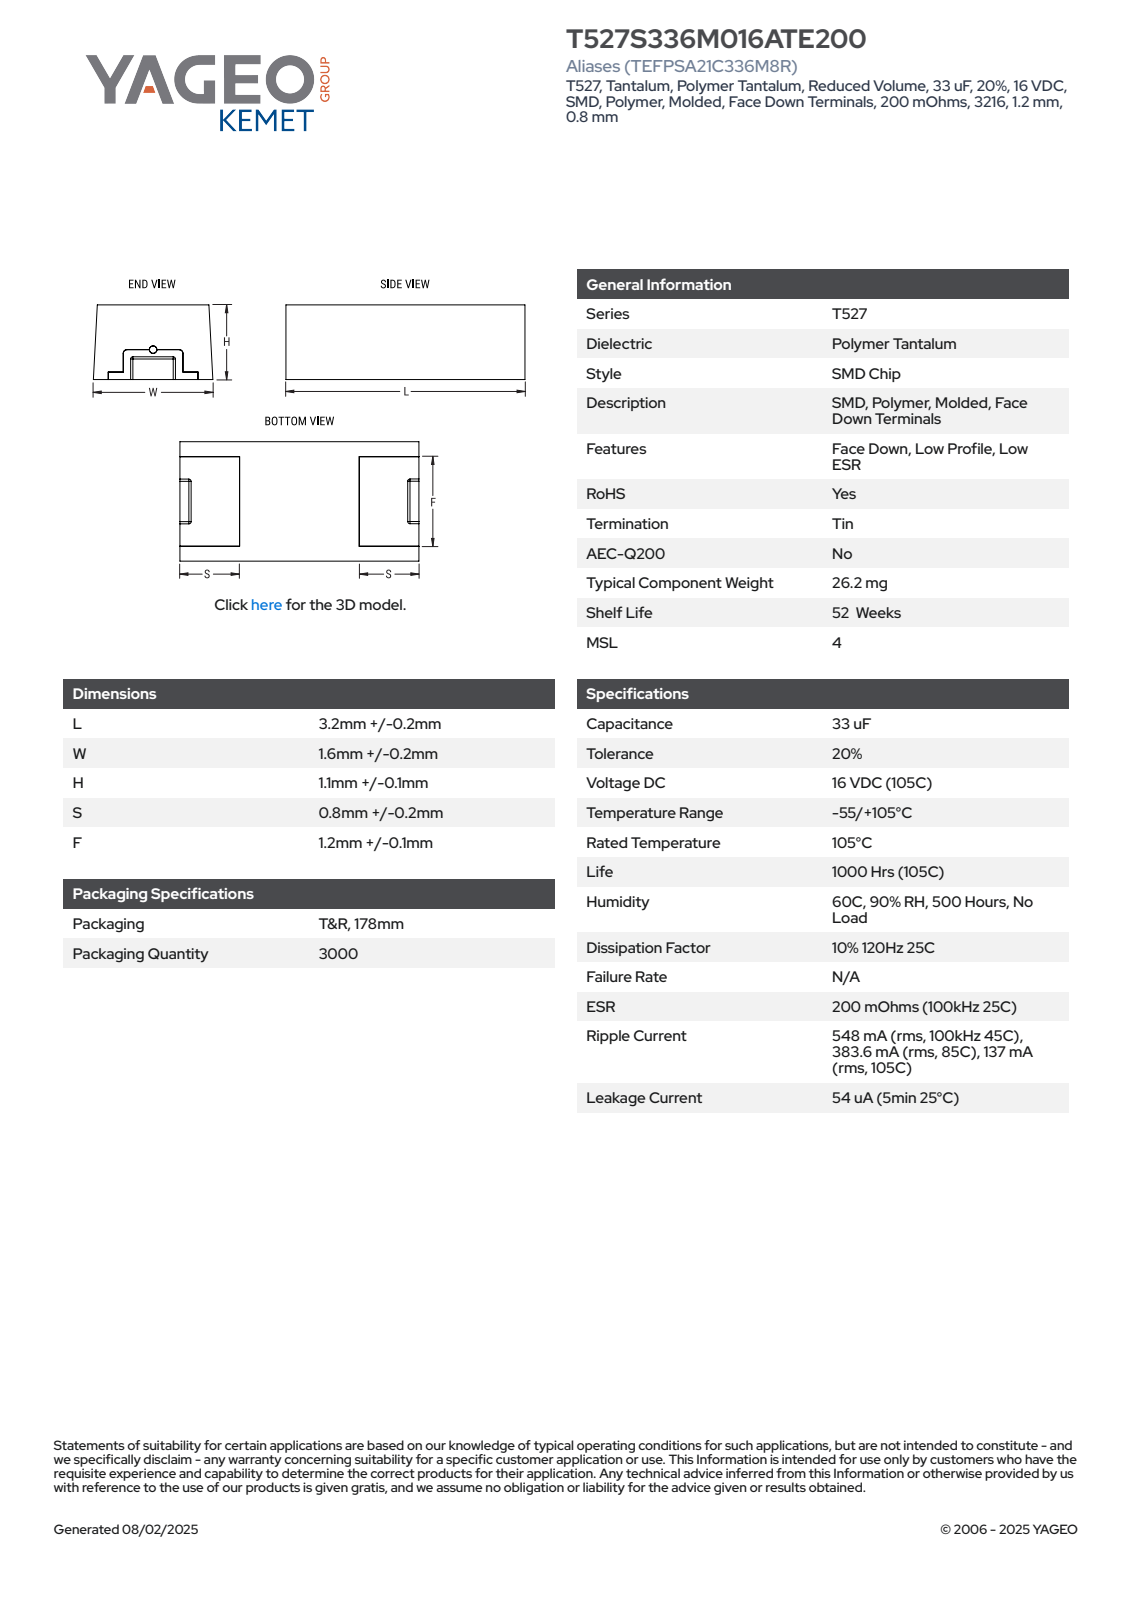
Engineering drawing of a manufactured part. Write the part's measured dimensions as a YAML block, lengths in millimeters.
part_name: "CTS_TCBFD_3216_L3.4W1.8H1.2S0.8F1.3"
step_written_by: "SolidWorks 2020 (AUTOMOTIVE_DESIGN)"
units: millimeters
bodies: {solids: 4, faces: 107, planar: 99, cylindrical: 8, other: 0}
overall_size: [3.4, 1.8, 1.21]
volume: 7
surface_area: 26
partial_cylinders:
  - {radius: 0.1, count: 4}
face_to_face_distances: [1.2, 1.8, 3.4, 1.55, 0.8, 2.6, 3.3, 0.7, 2.5, 1.3]
